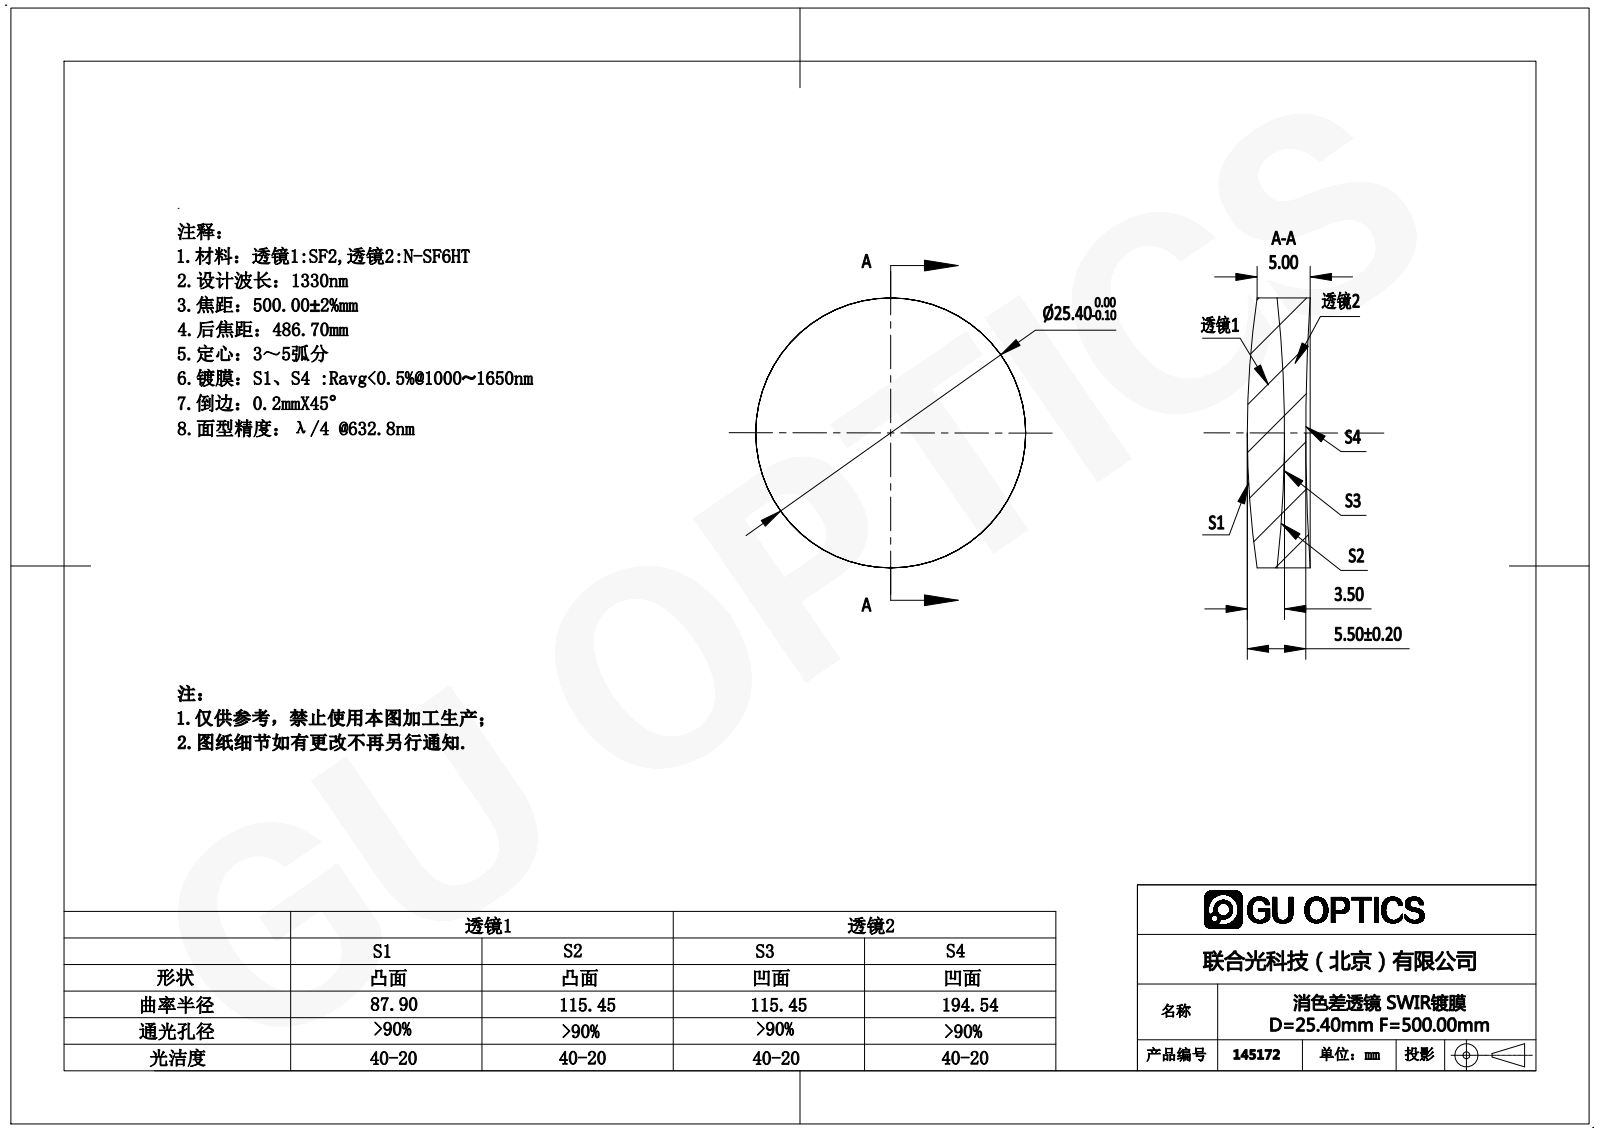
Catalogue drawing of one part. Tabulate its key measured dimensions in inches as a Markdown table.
| quantity | value |
| --- | --- |
| part name | 145172 |
| STEP written by | SolidWorks 2016 (AUTOMOTIVE_DESIGN) |
| units | inches |
| bodies | 2 solids, 12 faces (0 planar, 4 cylindrical, 8 other) |
| overall size | 1 × 1 × 0.233 |
| volume | 0.162 in³ |
| surface area | 3.77 in² |
| round bosses / shafts (diameter × count) | 1 × 1 |
